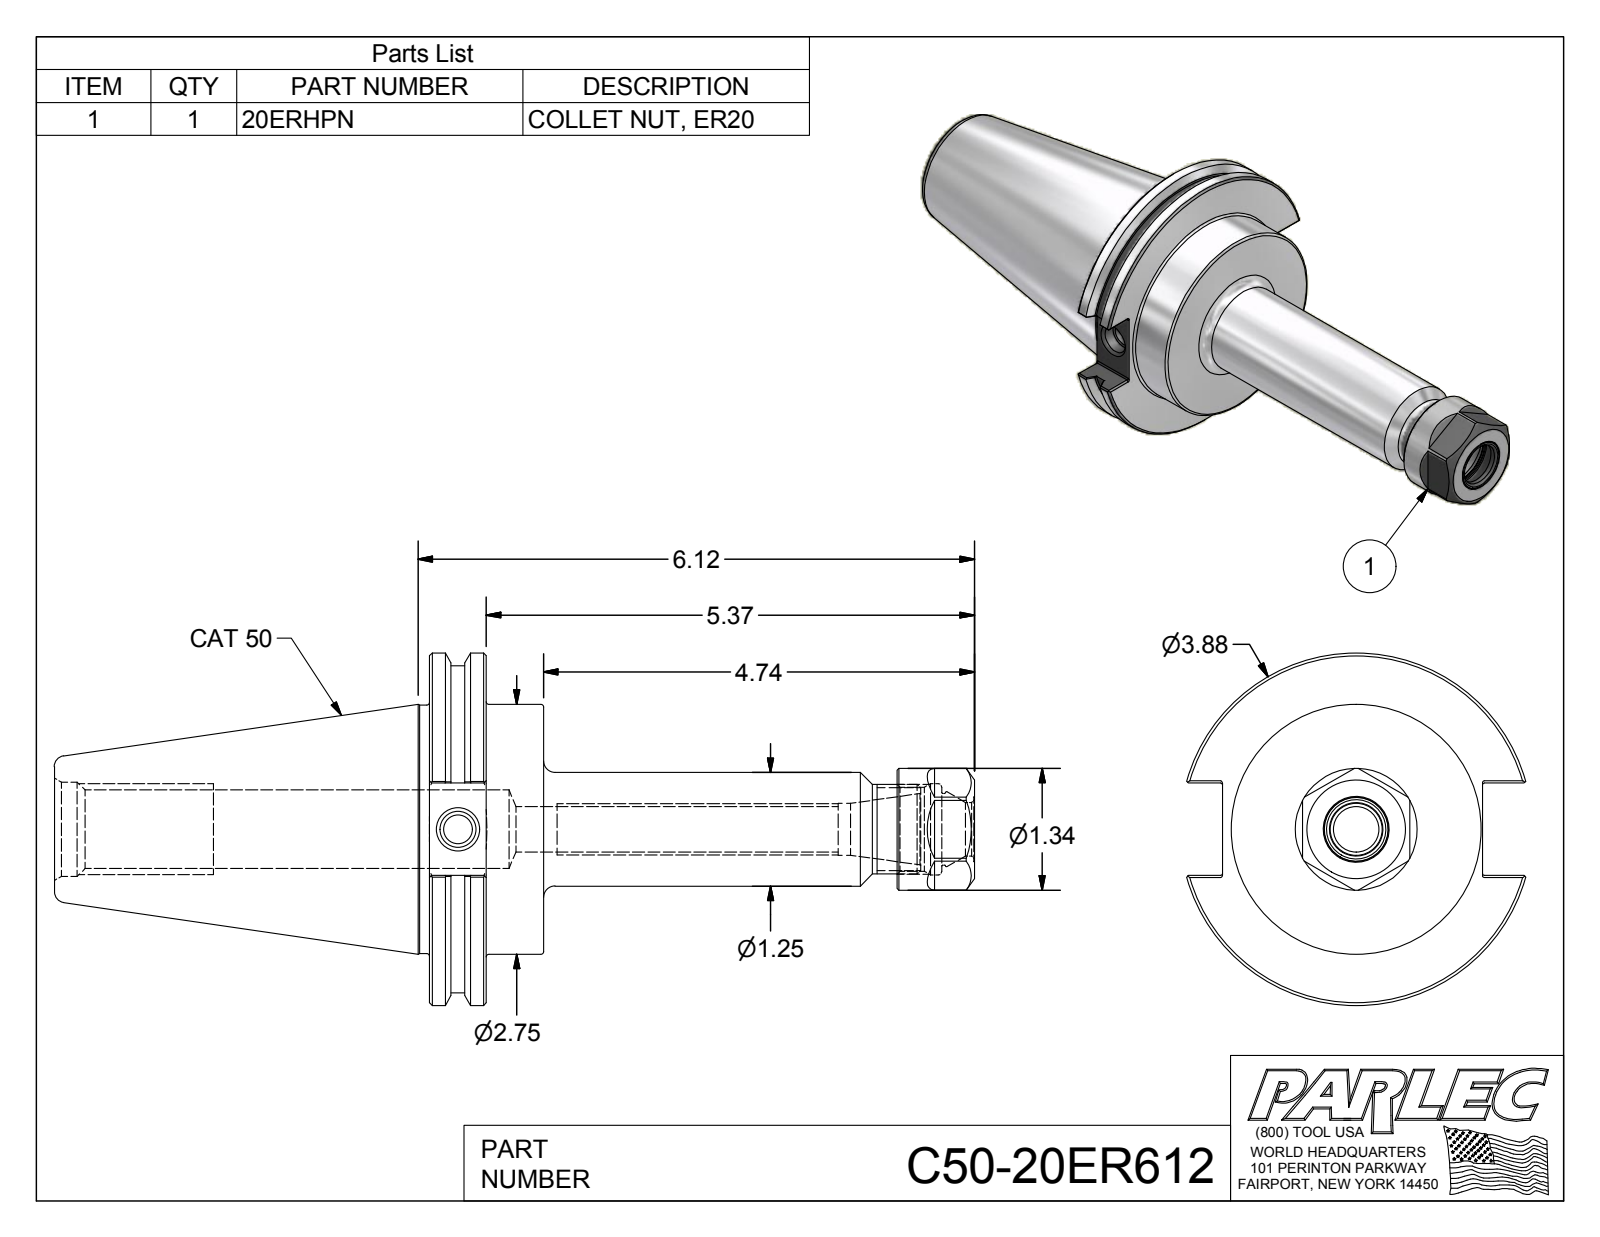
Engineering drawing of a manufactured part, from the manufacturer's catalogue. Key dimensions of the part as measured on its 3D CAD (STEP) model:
Part name (STEP PRODUCT): C50-20ER612; C50-20ER6-1; 20ERHPN
STEP written by: Autodesk Inventor 2012 (AUTOMOTIVE_DESIGN)
Units: inches
Bodies: 2 solids, 126 faces (49 planar, 33 cylindrical, 44 other)
Overall size (bounding box): 10.12 × 3.875 × 3.729
Volume: 27.35 in³ · Surface area: 104.8 in²
Round holes (diameter × count): ⌀0.315 ×1, ⌀0.399 ×1, ⌀0.502 ×1, ⌀0.57 ×1, ⌀0.587 ×1, ⌀0.79 ×1, ⌀0.865 ×1, ⌀0.926 ×1, ⌀1.005 ×1, ⌀1.038 ×1
Round bosses / shafts (diameter × count): ⌀3.875 ×1, ⌀3.594 ×1, ⌀2.75 ×1, ⌀2.73 ×1, ⌀1.34 ×1, ⌀1.25 ×1, ⌀0.984 ×1
Partial cylindrical surfaces — rounded edges, fillets, slot ends (radius × count): R0.02 ×12
Main face-to-face distances: 0.625, 1.255, 0.63, 1.18, 5.145, 4.52, 3.89, 5.995, 5.37, 4.74
